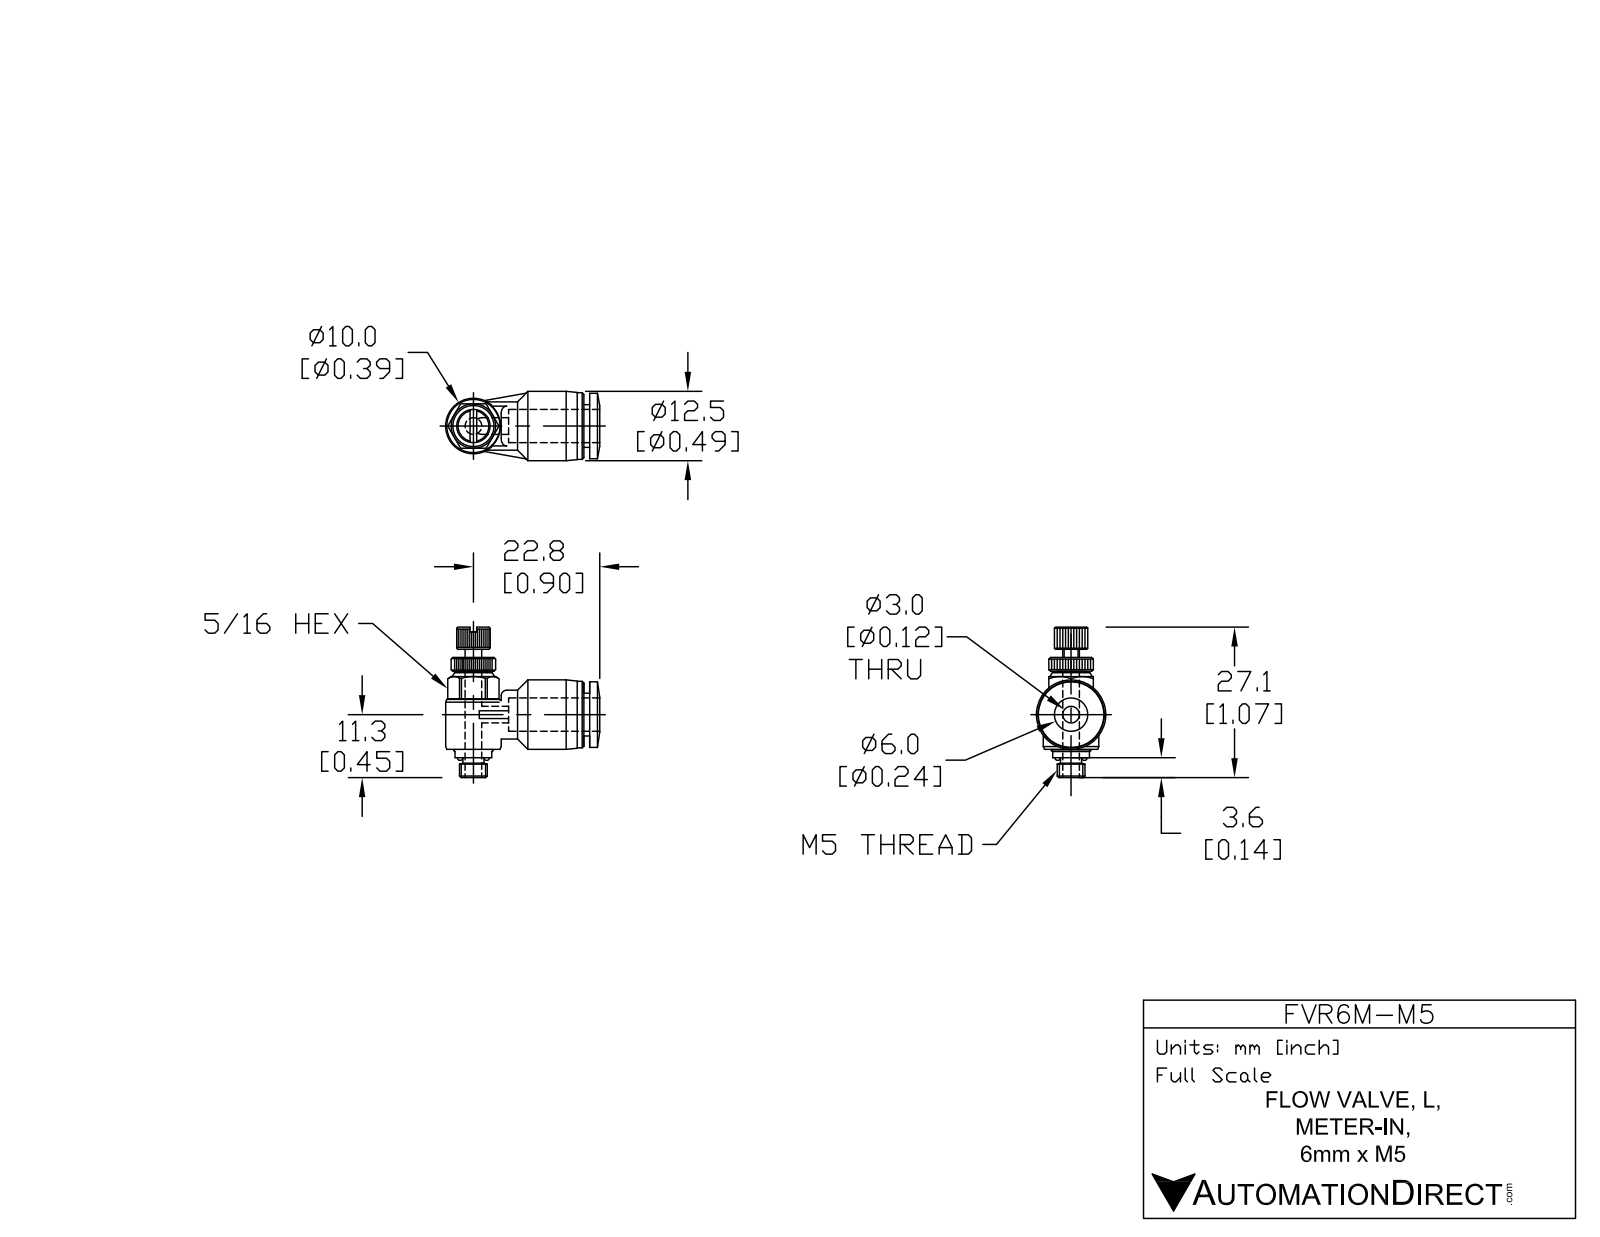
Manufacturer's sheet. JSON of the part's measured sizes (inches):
{"part_name": "FVR6M-M5", "step_written_by": "SolidWorks 2015 (AUTOMOTIVE_DESIGN)", "units": "inches", "bodies": {"solids": 2, "faces": 345, "planar": 152, "cylindrical": 97, "other": 96}, "overall_size": [1.146, 1.093, 0.492], "volume_in3": 0.159, "surface_area_in2": 3.616, "round_holes": [[0.079, 2], [0.15, 1], [0.248, 1]], "round_bosses_or_shafts": [[0.492, 1], [0.472, 1], [0.465, 1], [0.394, 1], [0.346, 1], [0.303, 1], [0.299, 1], [0.28, 1]], "partial_cylinders_radius": [[0.118, 1], [0.157, 1]], "face_to_face_distances": [0.041, 0.315, 0.652, 0.136, 0.575, 0.297, 0.157, 0.206, 0.433, 0.533]}
